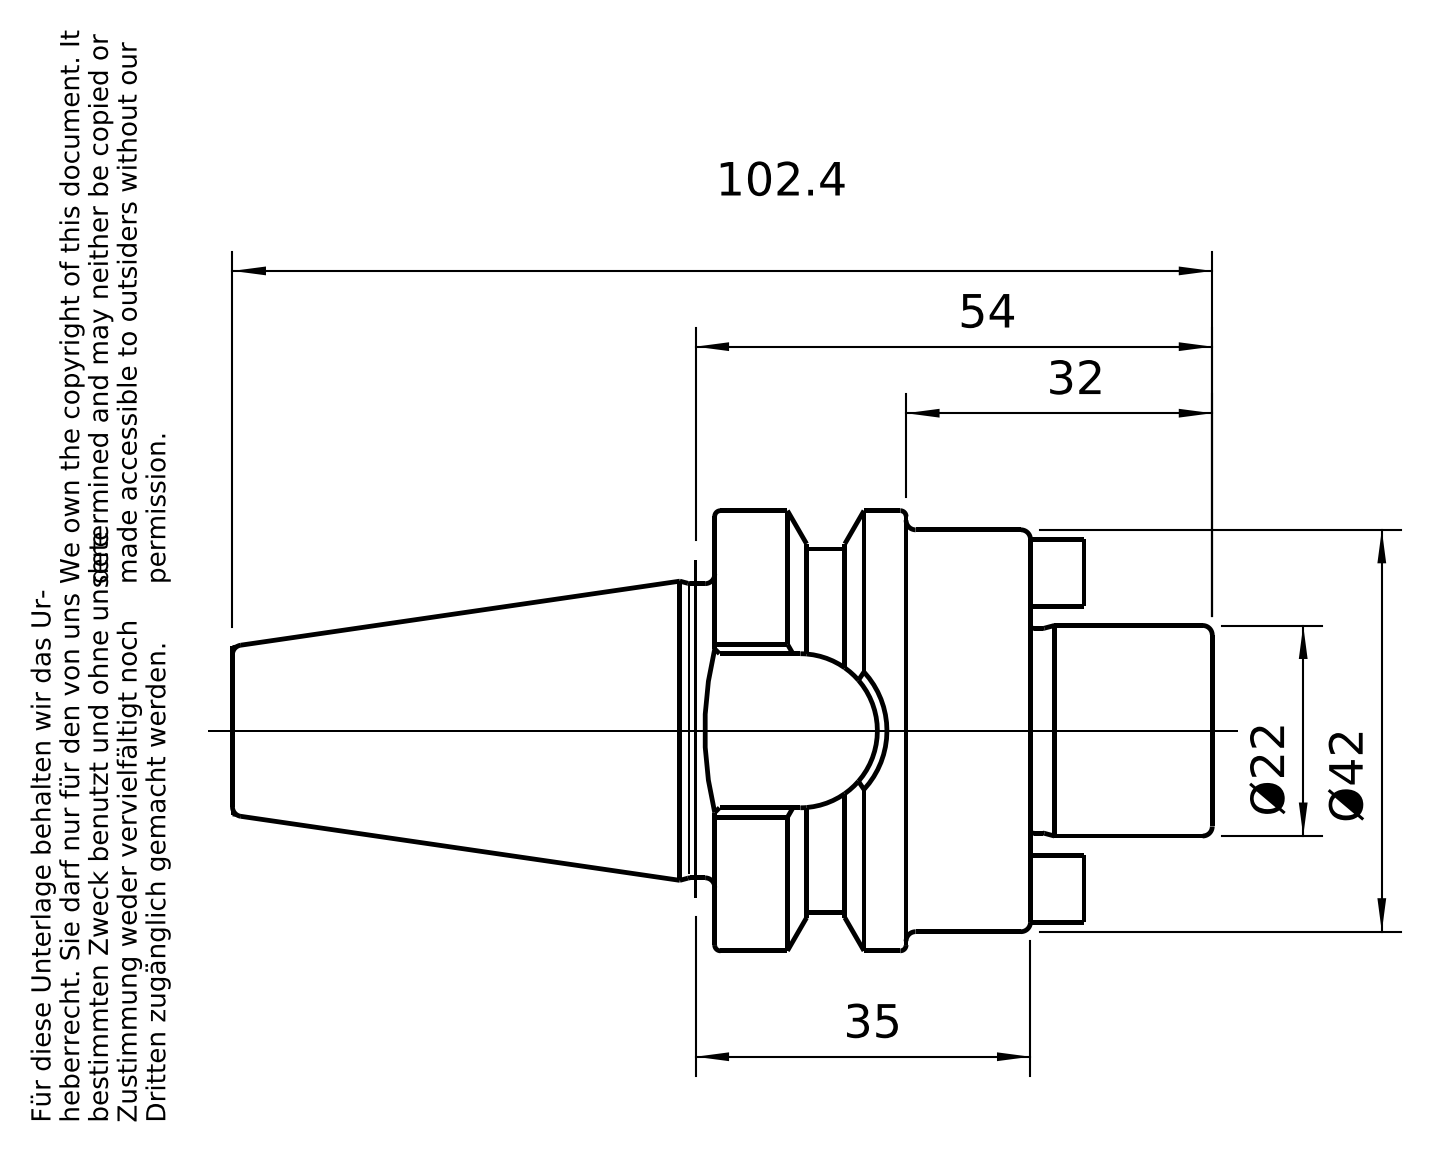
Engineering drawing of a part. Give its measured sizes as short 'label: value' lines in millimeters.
name: 30-550-22
written by: PRO/ENGINEER BY PARAMETRIC TECHNOLOGY CORPORATION, 2010430 (CONFIG_CONTROL_DESIGN)
unit: mm
bodies: 1 solid, 117 faces (41 planar, 26 cylindrical, 50 other)
size: 102.4 × 45.98 × 45.98
volume: 73 772 mm³; area: 16 678 mm²
holes: 1× ⌀8.5, 1× ⌀10, 1× ⌀10.11, 1× ⌀12.51, 1× ⌀13
bosses: 1× ⌀45.98, 1× ⌀42, 1× ⌀30.75, 1× ⌀22, 1× ⌀12.01
rounds: 1× R8.1, 1× R18.88
face distances: 33, 52, 19, 32.3, 38.6, 5.6, 13.4, 3.1, 13.1, 3.85
